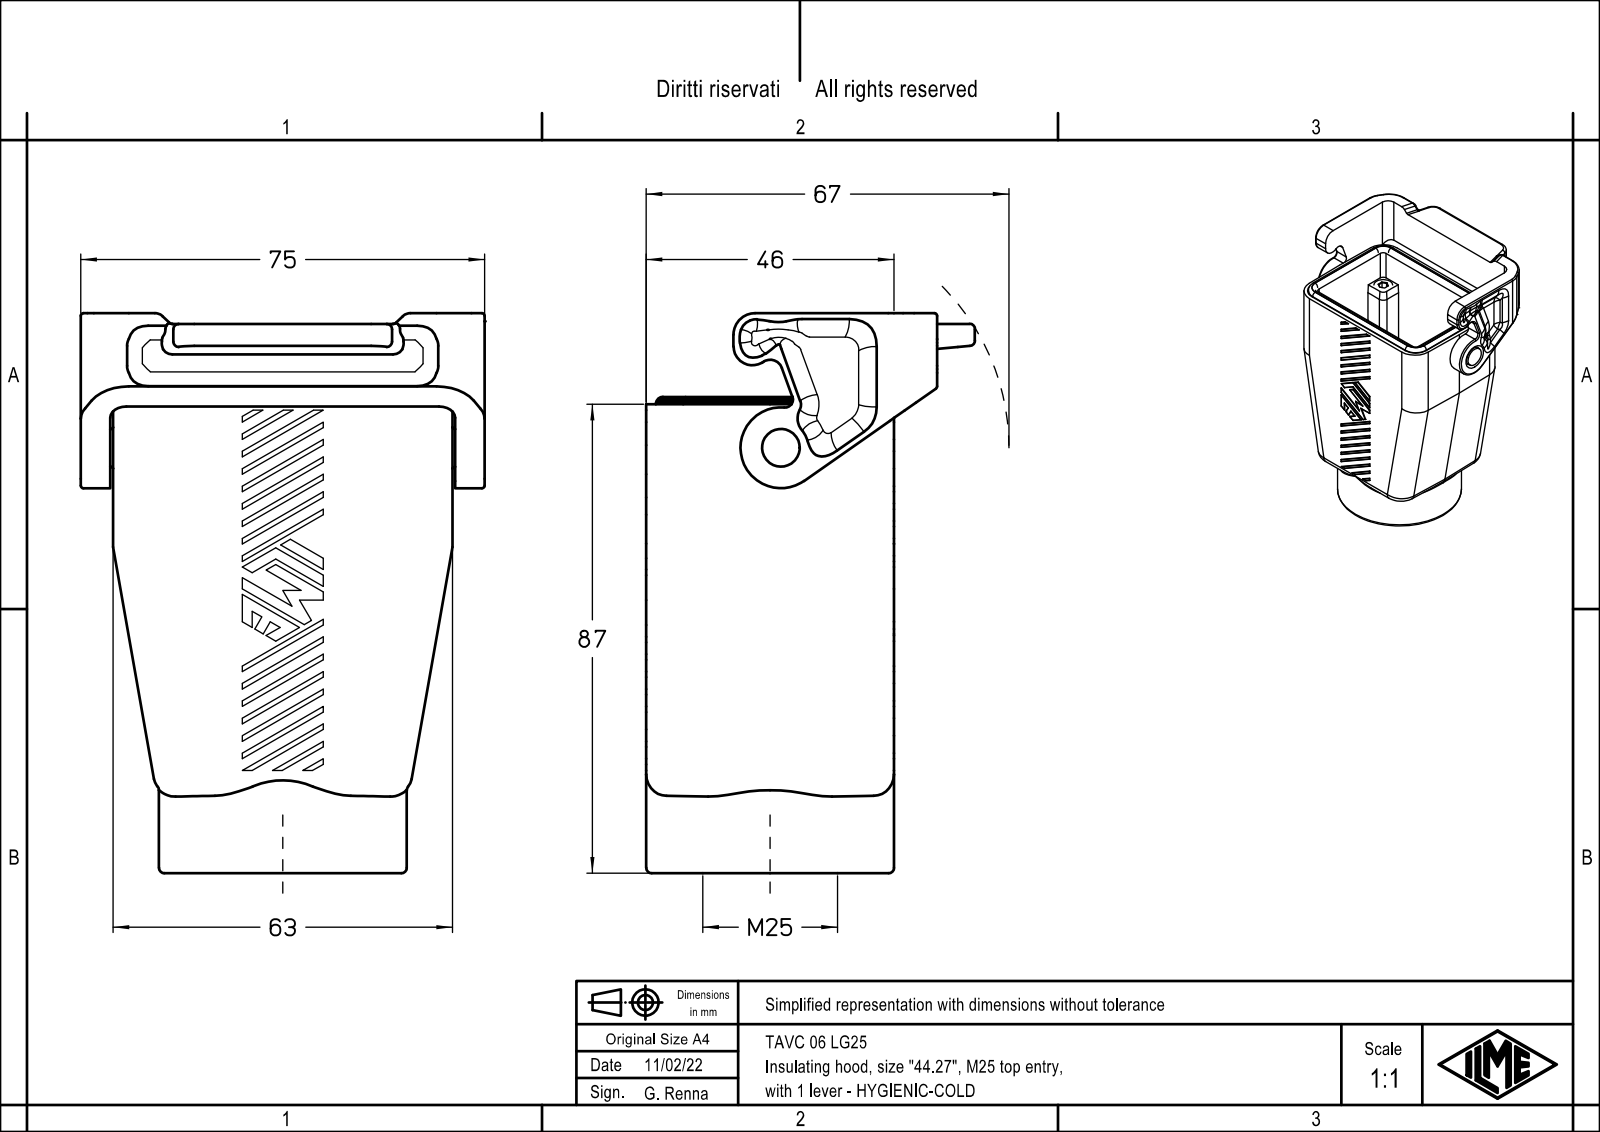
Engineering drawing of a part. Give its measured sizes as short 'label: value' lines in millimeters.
name: TAVH 06 LG25
written by: Creo Elements/Direct Modeling 20.1B 02-Apr-2019 (C) Parametric Technology GmbH (AUTOMOTIVE_DESIGN)
unit: mm
bodies: 1 solid, 546 faces (188 planar, 306 cylindrical, 52 other)
size: 103.9 × 75 × 61.15
volume: 116 497 mm³; area: 40 467 mm²
holes: 1× ⌀21, 1× ⌀23.6
bosses: 1× ⌀46, 1× ⌀7
rounds: 128× R0.15, 13× R3, 10× R2, 8× R1, 8× R1.3, 8× R7, 7× R1.5, 4× R6
face distances: 5.4, 40.6, 46, 35.2, 3, 20.5, 49, 43.6, 8.4, 63
